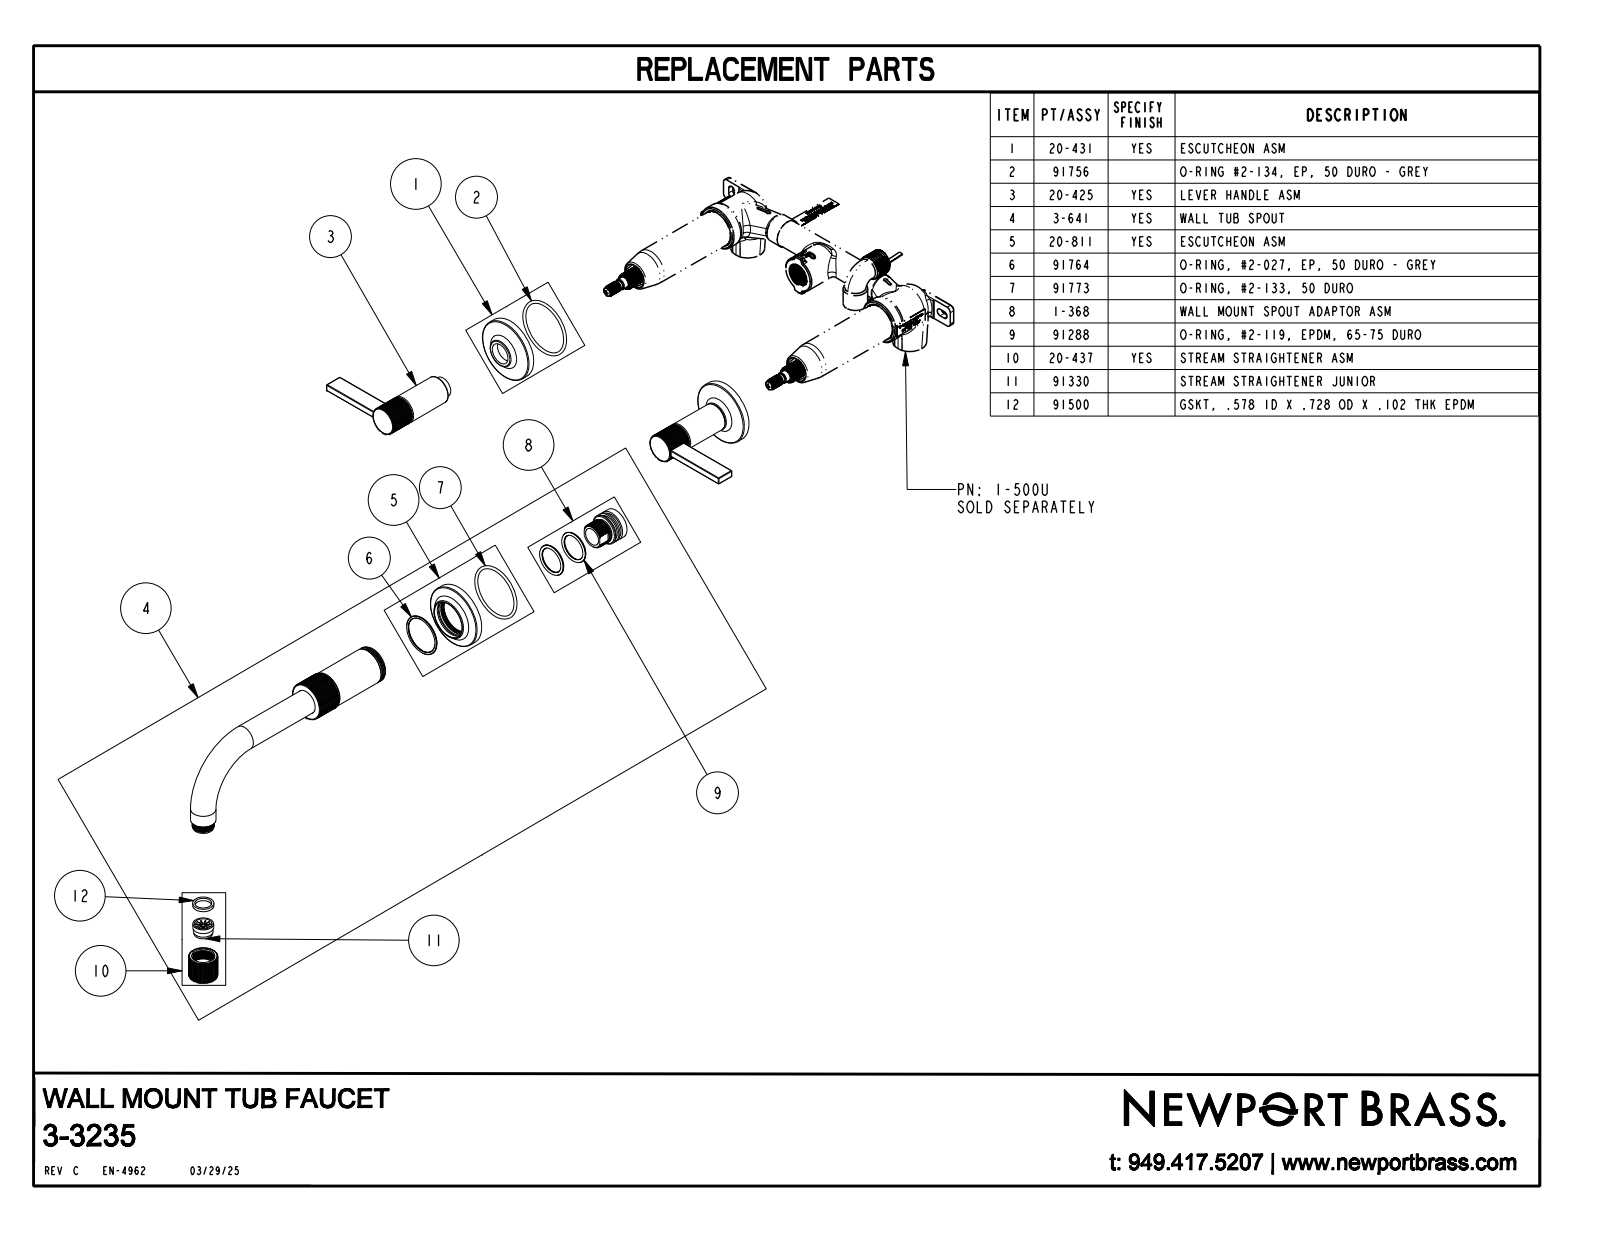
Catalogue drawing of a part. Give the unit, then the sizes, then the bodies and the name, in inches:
Units: inches
Overall size (bounding box): 13.475 × 10.385 × 8.75
Round bosses / shafts (diameter × count): ⌀2.25 ×3, ⌀1 ×2, ⌀0.875 ×2, ⌀0.85 ×2, ⌀0.52 ×2, ⌀1.312 ×1, ⌀1.28 ×1
Partial cylindrical surfaces — rounded edges, fillets, slot ends (radius × count): R0.02 ×20, R0.03 ×4, R0.437 ×2, R0.5 ×1, R0.675 ×1
Main face-to-face distances: 0.25, 3.201, 0.624, 0.623, 3.146, 0.055, 2.496, 0.65, 0.705, 2.24
Volume: 17.44 in³ · Surface area: 94.27 in²
Bodies: 3 solids, 1025 faces (611 planar, 348 cylindrical, 66 other)
Part name (STEP PRODUCT): 3-3235_SW0001
STEP written by: CREO PARAMETRIC BY PTC INC, 2018400 (AUTOMOTIVE_DESIGN)
